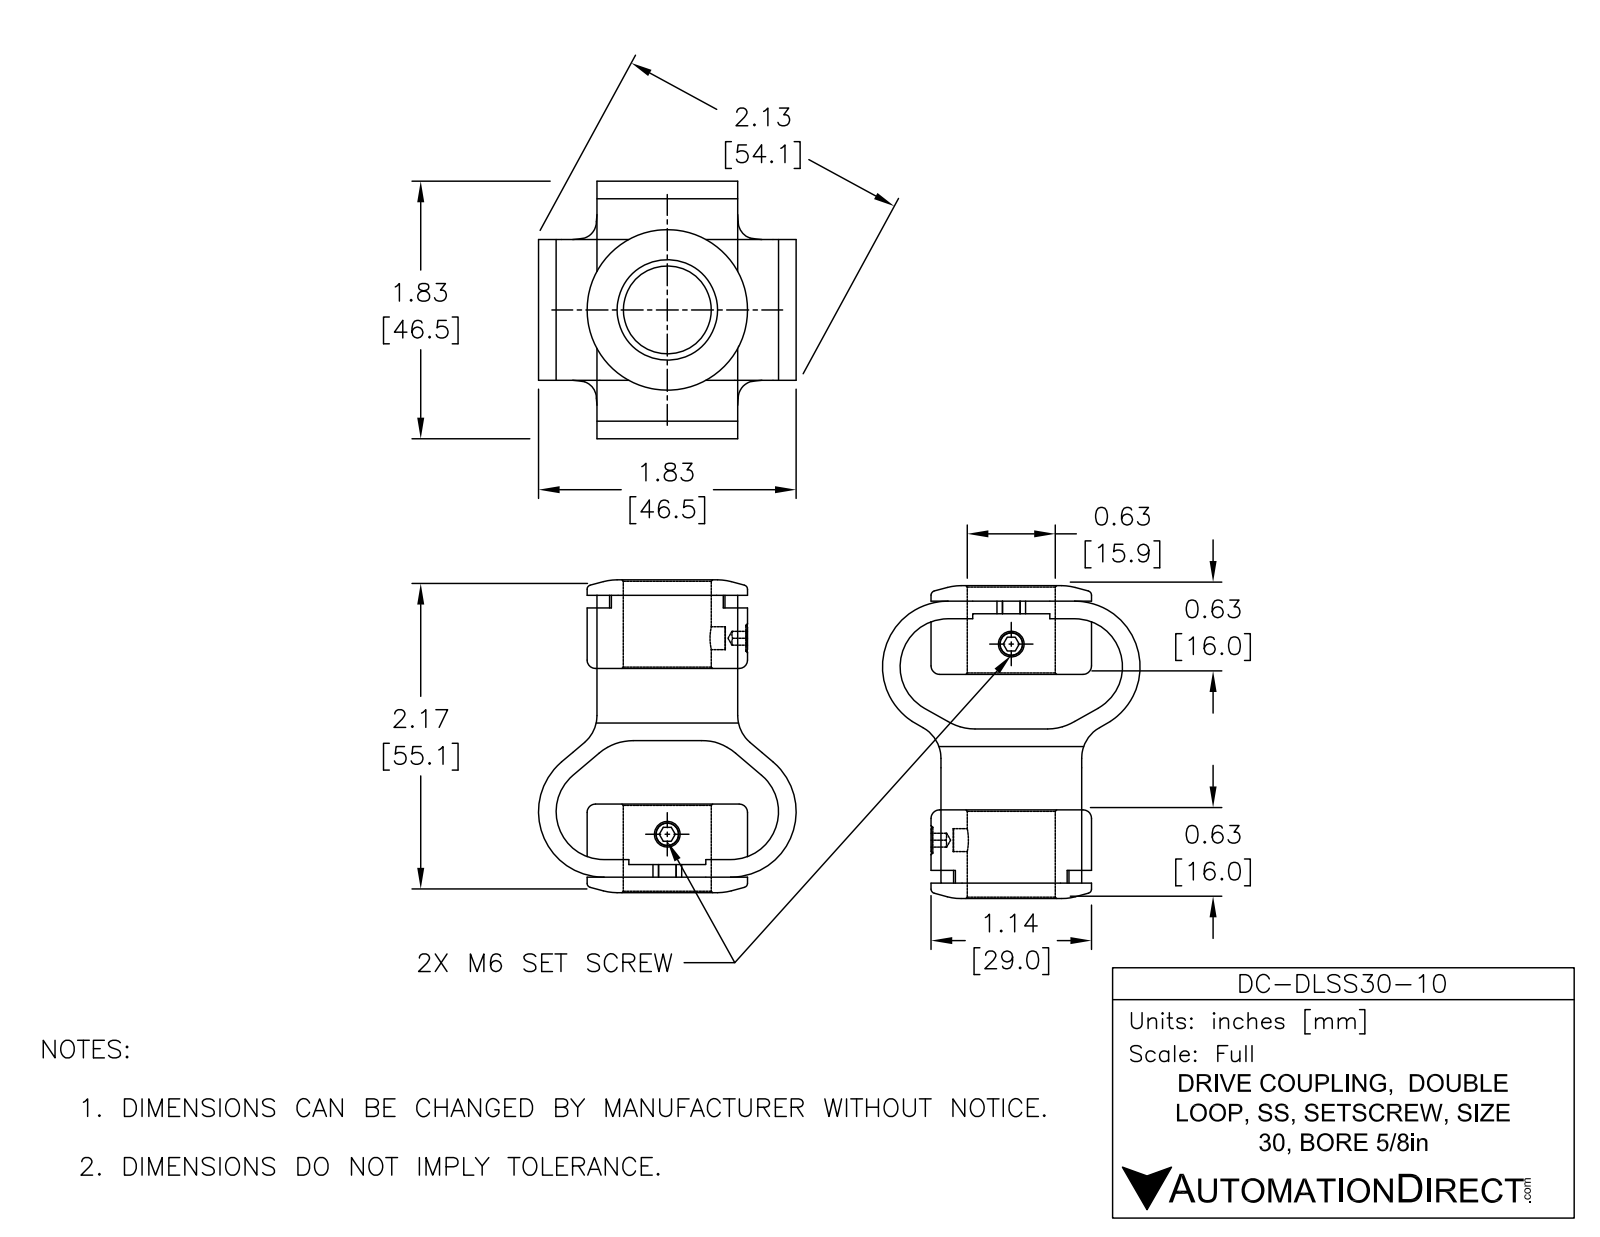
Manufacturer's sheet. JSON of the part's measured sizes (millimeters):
{"part_name": "DC-DLSS30-10", "step_written_by": "SolidWorks 2015 (AUTOMOTIVE_DESIGN)", "units": "millimeters", "bodies": {"solids": 1, "faces": 165, "planar": 88, "cylindrical": 37, "other": 40}, "overall_size": [56.46, 46.48, 46.48], "volume_mm3": 26069, "surface_area_mm2": 15027, "round_holes": [[5.26, 2], [15.88, 1]], "round_bosses_or_shafts": [[28.96, 1]], "partial_cylinders_radius": [[8.64, 4], [9.53, 4], [11.81, 4], [10.41, 1]], "face_to_face_distances": [25.4, 3.17, 14.61, 24.46, 9.85, 11.44, 13.02, 24.64, 37.67, 26.23]}
